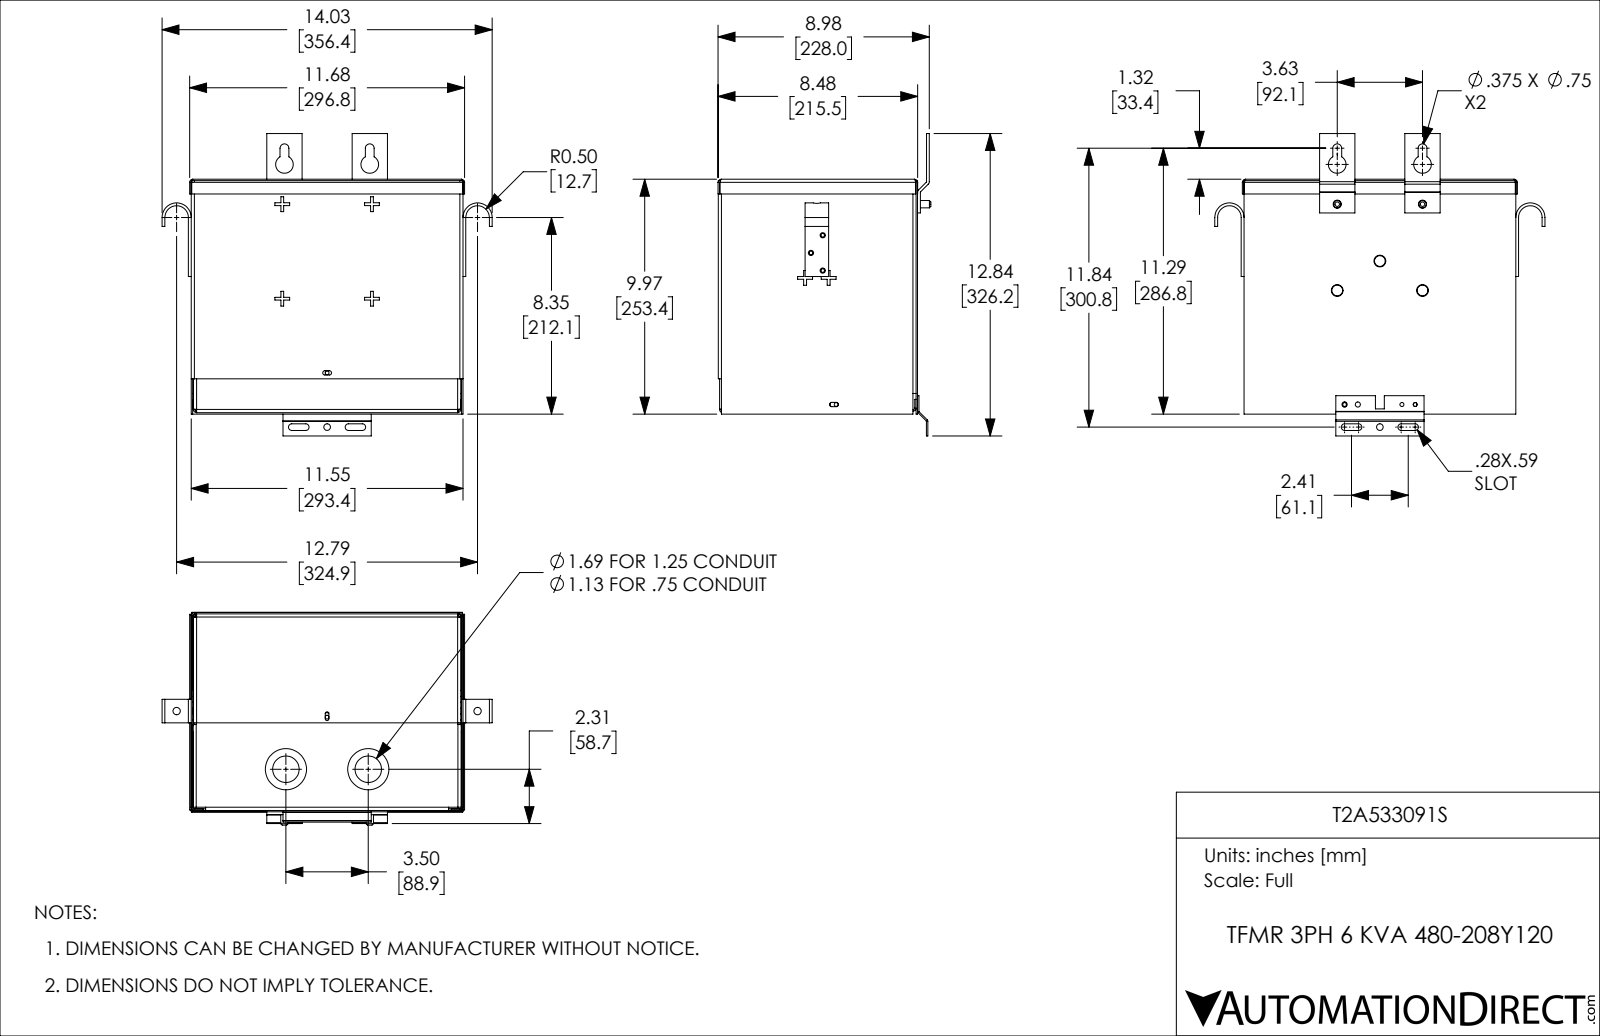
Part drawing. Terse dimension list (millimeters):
name: T2A533091S
written by: SolidWorks 2017 (AUTOMOTIVE_DESIGN)
unit: mm
bodies: 12 solids, 602 faces (392 planar, 138 cylindrical, 72 other)
size: 356.4 × 326.2 × 229.7
volume: 668 800 mm³; area: 869 700 mm²
holes: 5× ⌀4.1, 2× ⌀4.4, 2× ⌀5.6, 2× ⌀7.1, 2× ⌀8, 2× ⌀8.7, 2× ⌀19.1, 2× ⌀44.5, 1× ⌀4.4, 1× ⌀4.7, 1× ⌀28.6, 1× ⌀28.6
bosses: 2× ⌀47.5, 2× ⌀31.6, 2× ⌀7.9
rounds: 16× R1.9, 16× R3.4, 8× R2.4, 4× R3.6, 2× R0.5, 2× R0.8, 2× R2, 2× R2
face distances: 1.5, 213.6, 212.1, 250.3, 215.1, 1.5, 291.9, 1.7, 248.7, 293.4
hole spacings: 14.3, 34.1, 41.6, 42.8, 45.2, 51.2, 61.9, 71.7
